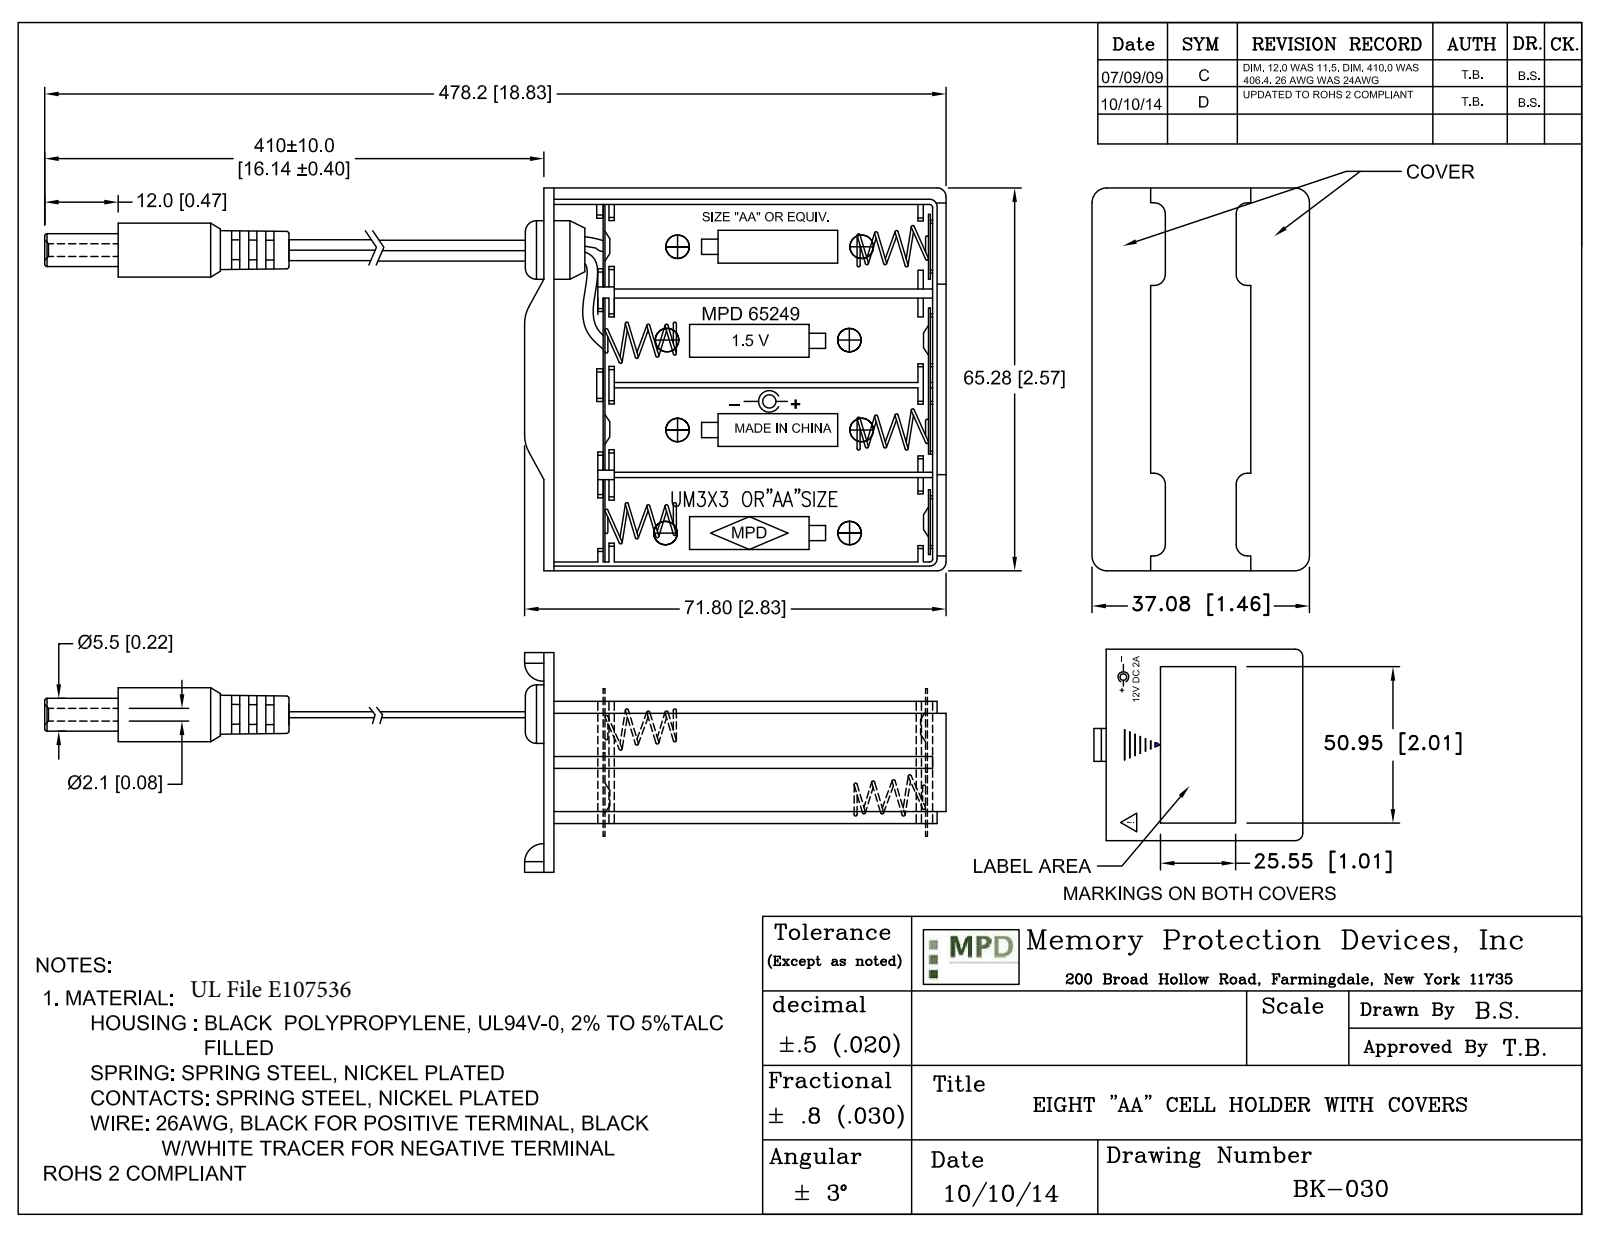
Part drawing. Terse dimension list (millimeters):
name: BK-030
written by: SolidWorks 2017 (AUTOMOTIVE_DESIGN)
unit: mm
bodies: 17 solids, 1165 faces (842 planar, 179 cylindrical, 144 other)
size: 478.2 × 65.28 × 37.08
volume: 45 918 mm³; area: 66 013 mm²
holes: 8× ⌀3.5, 1× ⌀2.1, 1× ⌀9.2
bosses: 8× ⌀4.3, 8× ⌀0.91, 1× ⌀11, 1× ⌀6.5, 1× ⌀5.5
rounds: 16× R2, 10× R0.7, 4× R7.77, 4× R9.31, 2× R1.6, 2× R2.5, 2× R3.4, 2× R5
face distances: 1.3, 16.29, 18.19, 2.3, 19.49, 17.59, 35.78, 1.9, 65.9, 34.48
hole spacings: 15.19, 31.51, 32, 35.42, 44.91, 16.32, 35.92, 46.7
